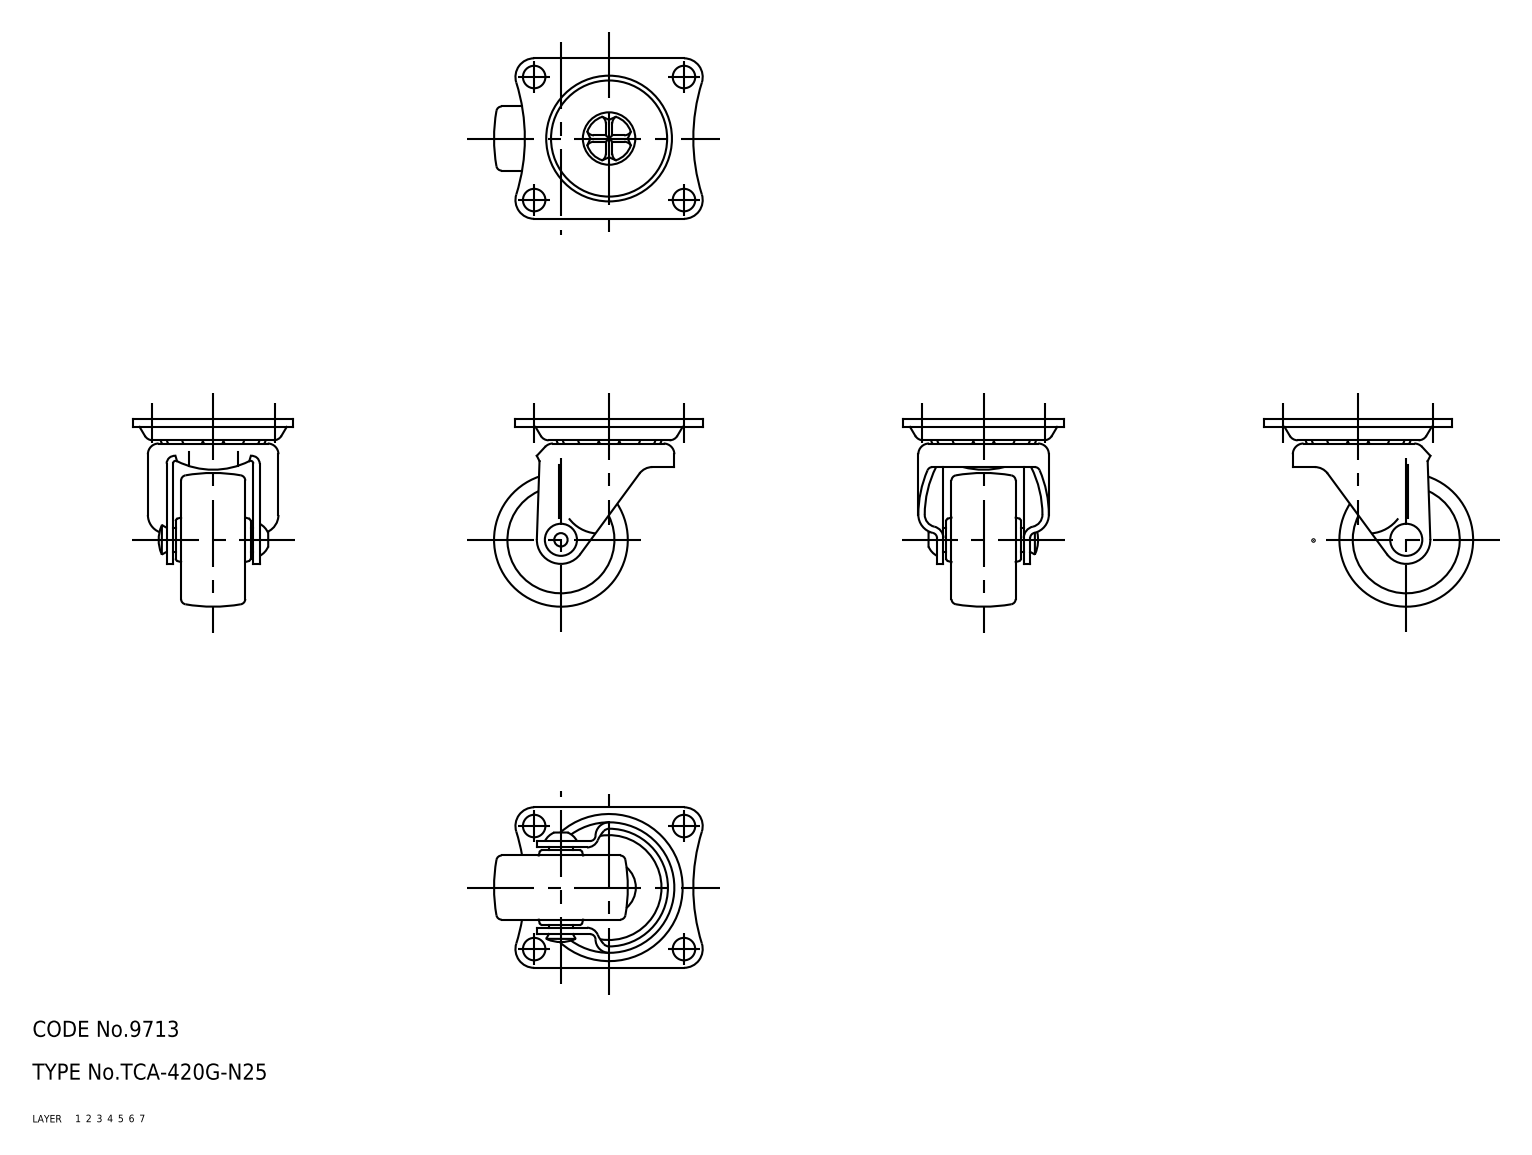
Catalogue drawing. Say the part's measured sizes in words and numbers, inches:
The part is named "wheel; mounting plate; main shaft; axle (+1 more)". Its 3-D file was written by "CADfix (AUTOMOTIVE_DESIGN)". It is 5 solids with 238 faces: 0 planar, 0 cylindrical and 238 other. Overall it measures 1.535 by 1.378 by 1.181 inches. Its volume is 0.496 cubic inches and its surface area 12.98 square inches.
